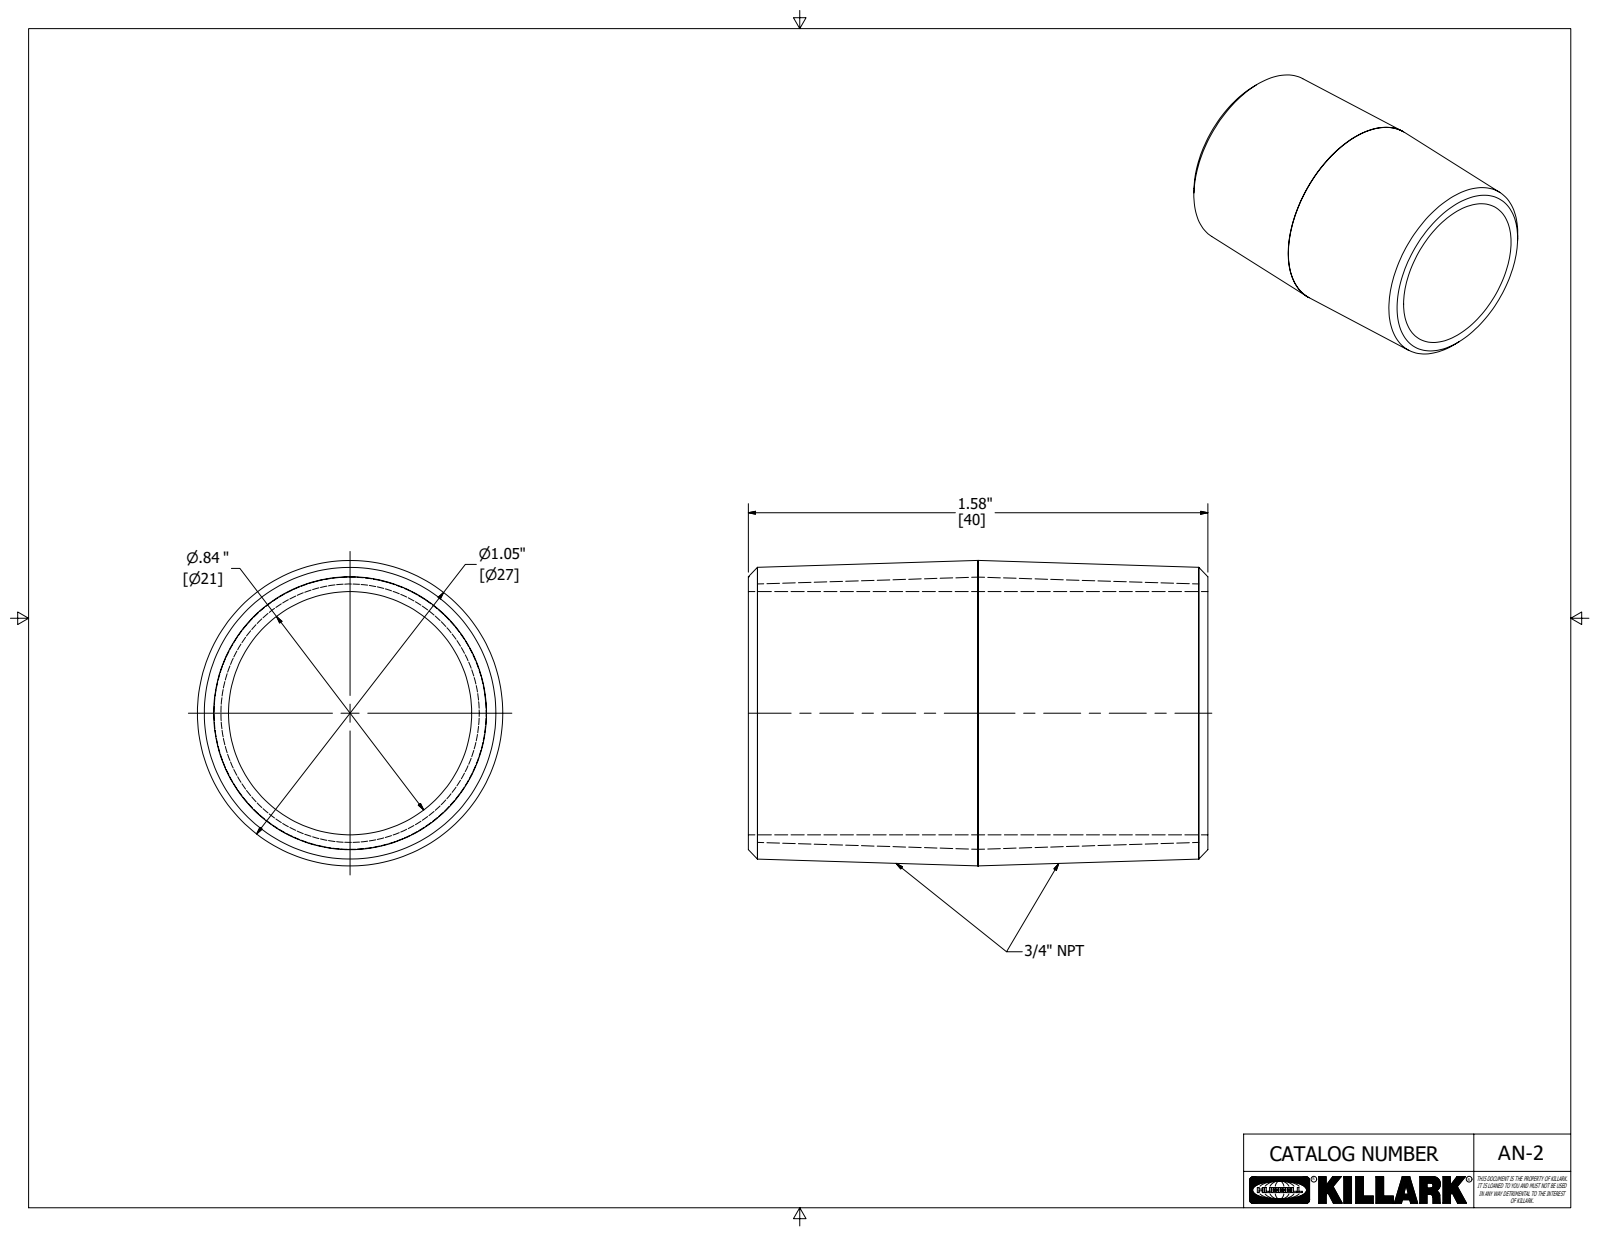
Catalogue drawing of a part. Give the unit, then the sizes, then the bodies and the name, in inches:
Units: inches
Overall size (bounding box): 1.58 × 1.05 × 1.05
Round holes (diameter × count): ⌀0.836 ×1
Round bosses / shafts (diameter × count): ⌀1.05 ×1
Main face-to-face distances: 1.58
Volume: 0.435 in³ · Surface area: 9.603 in²
Bodies: 1 solid, 8 faces (2 planar, 2 cylindrical, 4 other)
Part name (STEP PRODUCT): 14077-2
STEP written by: Autodesk Inventor 2020 (AUTOMOTIVE_DESIGN)
